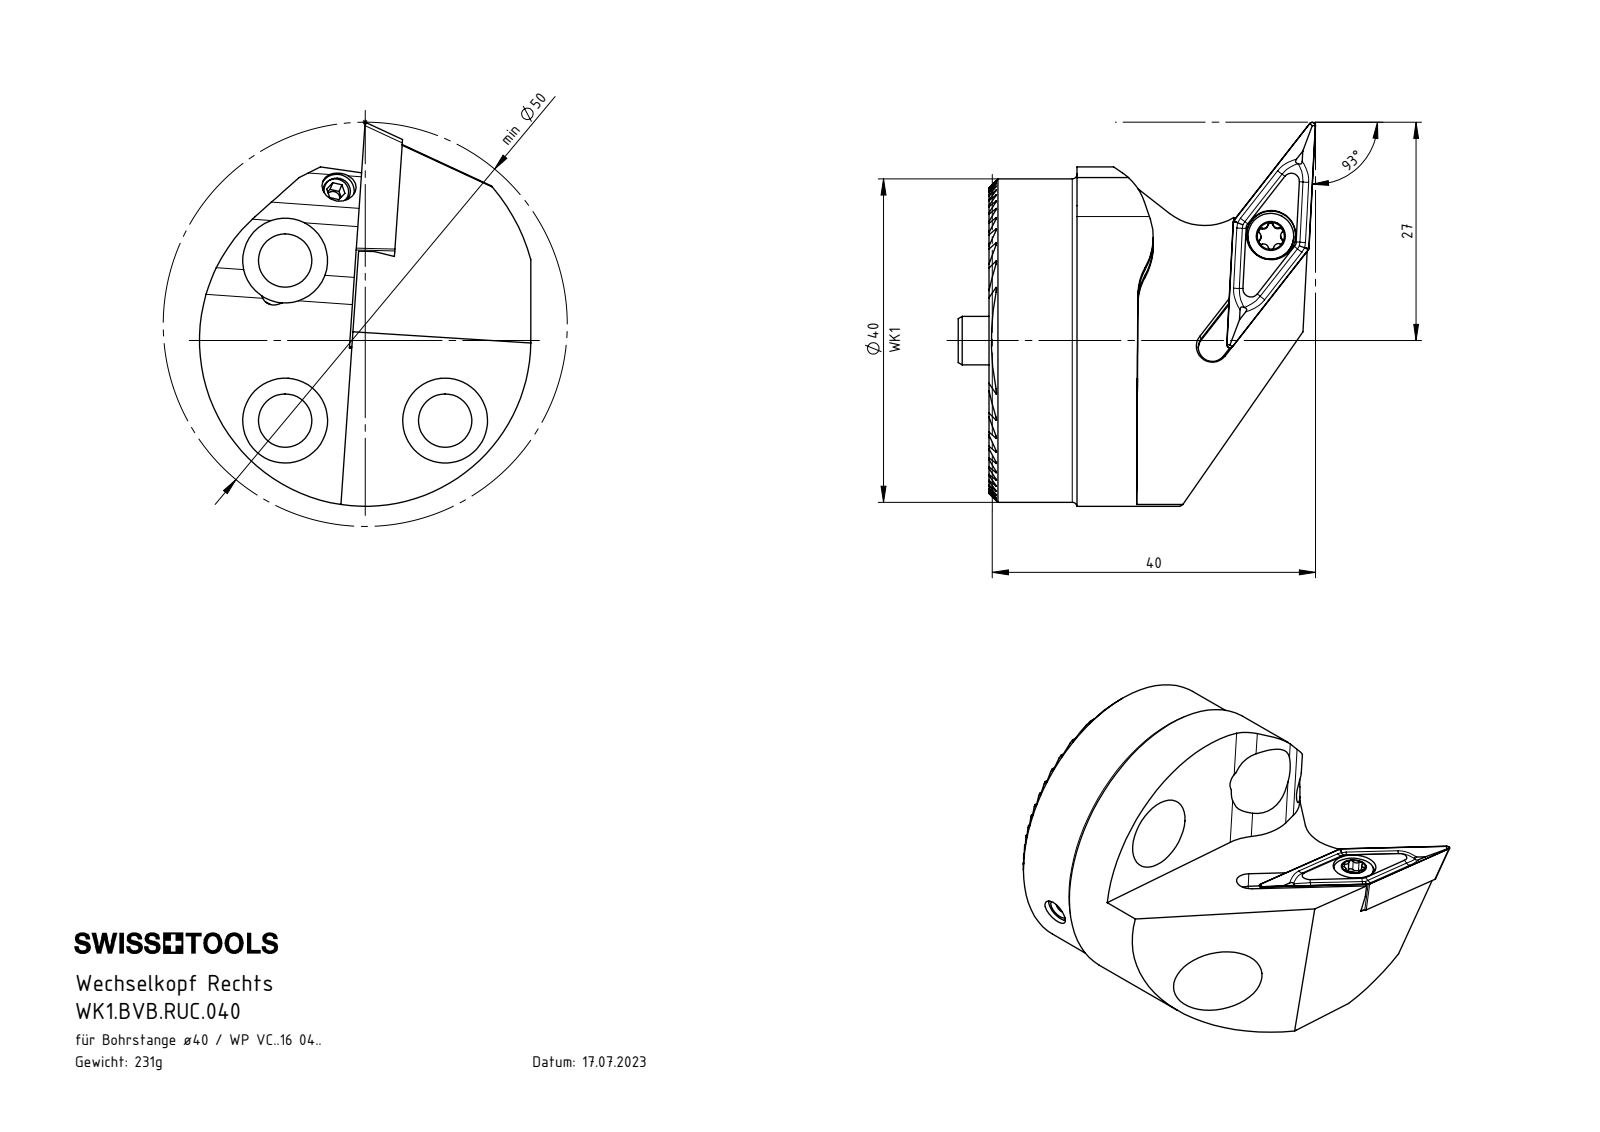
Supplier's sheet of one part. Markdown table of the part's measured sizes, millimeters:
| quantity | value |
| --- | --- |
| part name | WCB-ER2.001.009_B; VCMT160404; KVT_MB_600_040; WK1-BVB.RUC.040_A_Fertigbearbeitung (+3 more) |
| STEP written by | SolidWorks 2017 (AUTOMOTIVE_DESIGN) |
| units | millimeters |
| bodies | 10 solids, 573 faces (220 planar, 203 cylindrical, 150 other) |
| overall size | 47.5 × 44.2 × 41 |
| volume | 28 939 mm³ |
| surface area | 12 113 mm² |
| round holes (diameter × count) | 3.3 × 5, 4.2 × 3, 6.6 × 3, 10.5 × 3, 1.7 × 2, 3 × 2, 4 × 2, 4.4 × 1, 6.1 × 1, 12 × 1 |
| round bosses / shafts (diameter × count) | 4 × 5, 40 × 1, 6 × 1, 5.67 × 1, 3.8 × 1 |
| partial cylindrical surfaces (radius × count) | 0.12 × 26, 0.34 × 6, 0.59 × 6, 7 × 2, 8 × 2, 1.75 × 1, 20.5 × 1, 23 × 1 |
| main face-to-face distances | 1.3, 2.6, 3.9, 12.99, 5.2, 11.69, 9.09, 10.39, 7.79, 6.5 |
| hole center spacings | 14, 19.8, 28 |
